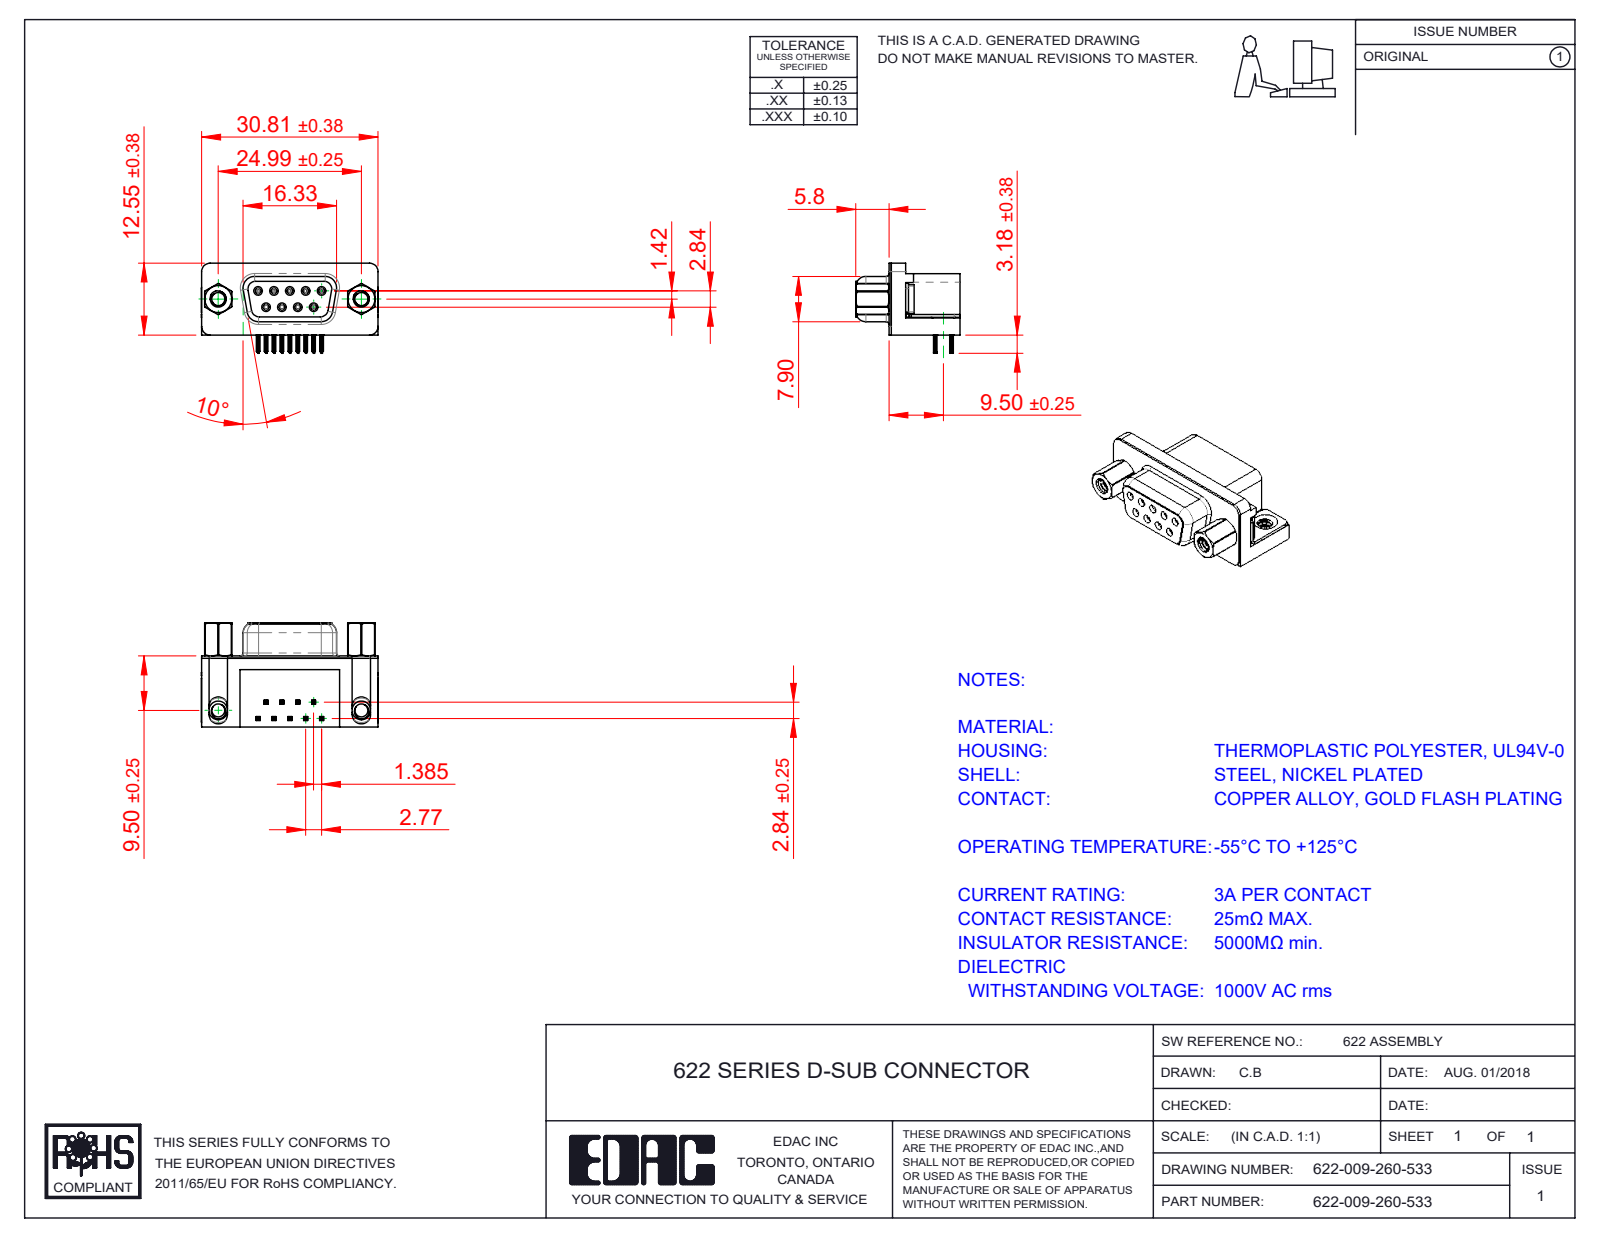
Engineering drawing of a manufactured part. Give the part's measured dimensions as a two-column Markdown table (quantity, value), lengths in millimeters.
| quantity | value |
| --- | --- |
| part name | 622 Housing_9 Socket; 622 4-40 Threaded Rivet; 622 Shell_9 Socket; 622 2 Prong Board Lock (+4 more) |
| STEP written by | SolidWorks 2016 (CONFIG_CONTROL_DESIGN) |
| units | millimeters |
| bodies | 17 solids, 1732 faces (738 planar, 488 cylindrical, 506 other) |
| overall size | 30.89 × 18.2 × 16.25 |
| volume | 3 927 mm³ |
| surface area | 5 532 mm² |
| round holes (diameter × count) | 0.8 × 9, 0.9 × 9, 2.26 × 2, 2.29 × 2, 4 × 2, 4.8 × 2, 5 × 2 |
| round bosses / shafts (diameter × count) | 1.2 × 9, 4.9 × 2, 4.75 × 2, 3.9 × 2, 2.79 × 2 |
| partial cylindrical surfaces (radius × count) | 0.1 × 72, 0.15 × 36, 0.35 × 18, 1 × 18, 0.5 × 10, 0.34 × 9, 0.25 × 8, 1.35 × 8 |
| main face-to-face distances | 0.4, 12, 12.4, 6.2, 0.35, 2.9, 2.5, 10.34, 0.5, 5.8 |
| hole center spacings | 3.16, 2.77, 5.54, 5.03, 5.04, 8.31, 7.48, 7.49 |
